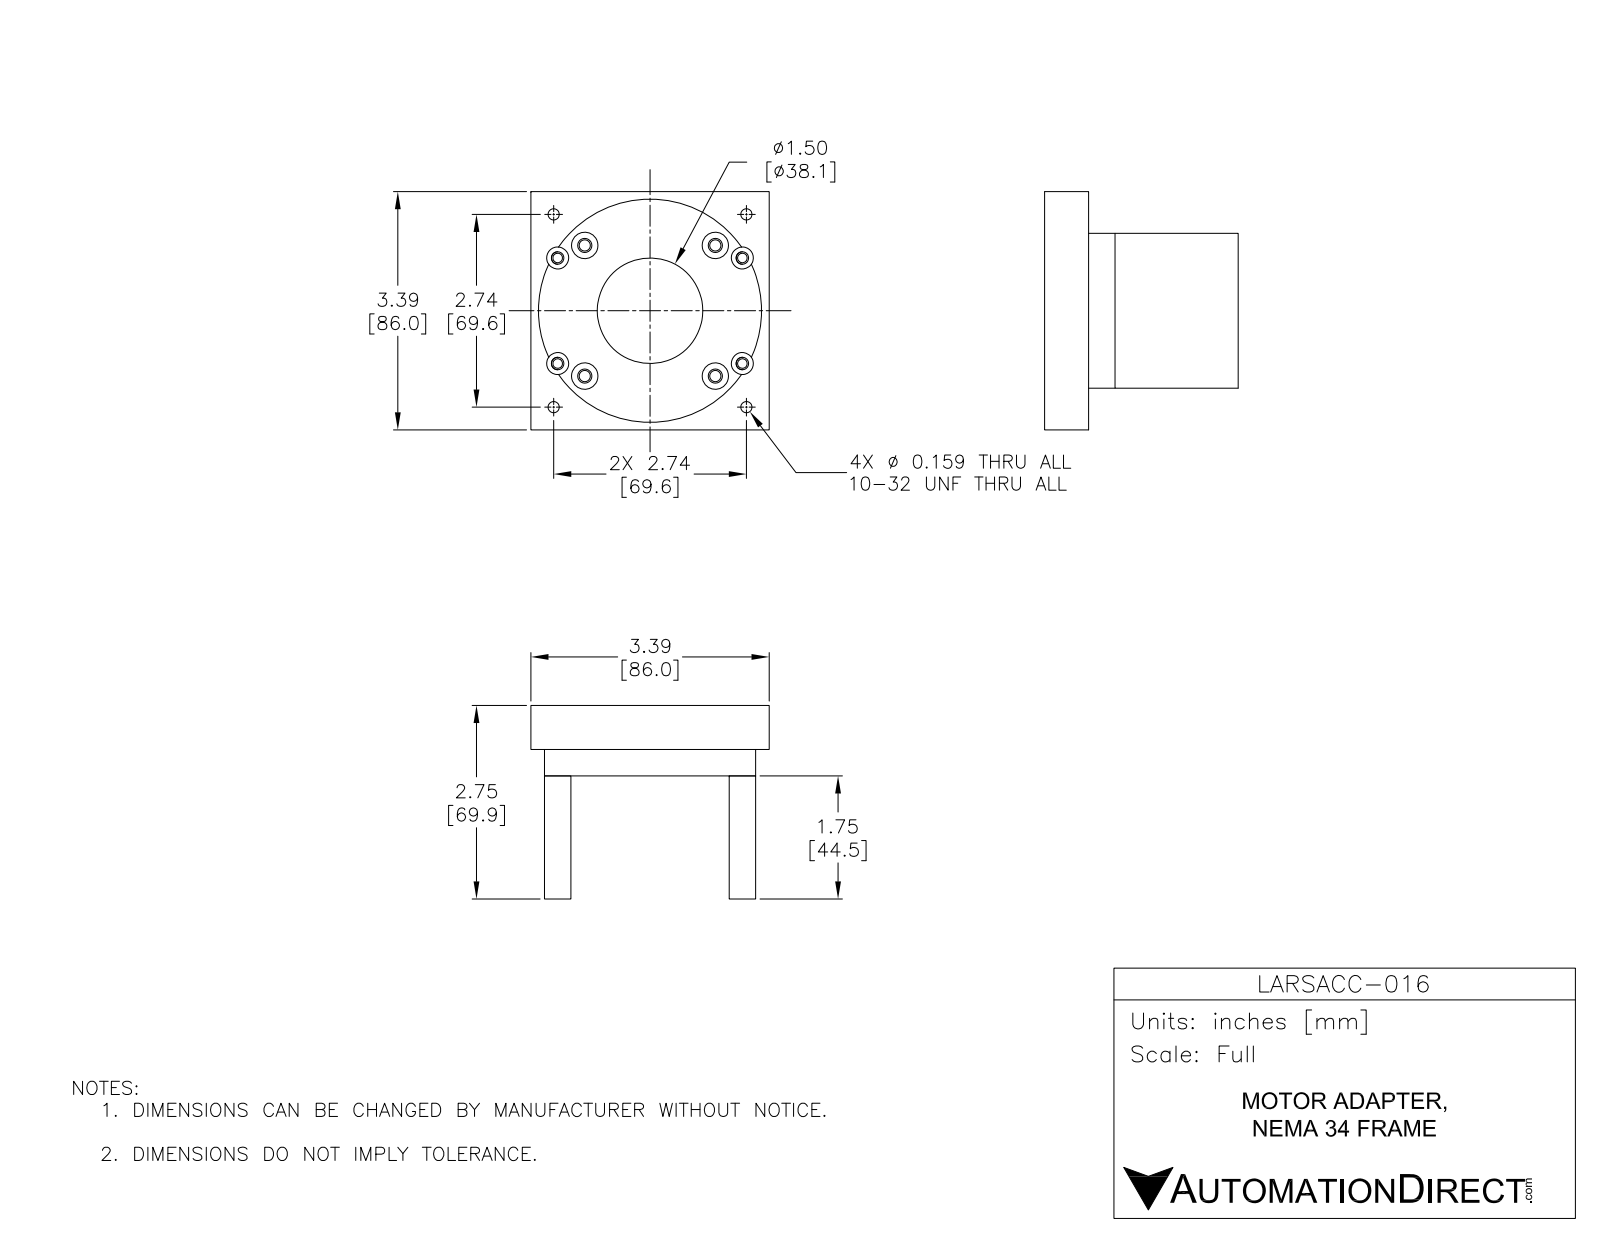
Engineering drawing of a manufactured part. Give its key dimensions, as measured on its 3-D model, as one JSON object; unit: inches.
{"part_name": "LARSACC-016", "step_written_by": "SolidWorks 2018 (AUTOMOTIVE_DESIGN)", "units": "inches", "bodies": {"solids": 4, "faces": 108, "planar": 39, "cylindrical": 69, "other": 0}, "overall_size": [3.386, 3.386, 2.75], "volume_in3": 9.597, "surface_area_in2": 74.45, "round_holes": [[0.159, 14], [0.177, 4], [0.201, 4], [0.313, 4], [0.375, 4], [1.5, 1], [1.504, 1], [3.17, 1]], "face_to_face_distances": [0.375, 0.875, 0.5, 2.625, 3, 0.193, 3.193, 0.375, 2.625, 2.25], "hole_center_spacings": [0.622, 1.5, 2.12, 2.625, 2.34, 0.25, 1.25, 1.722]}
